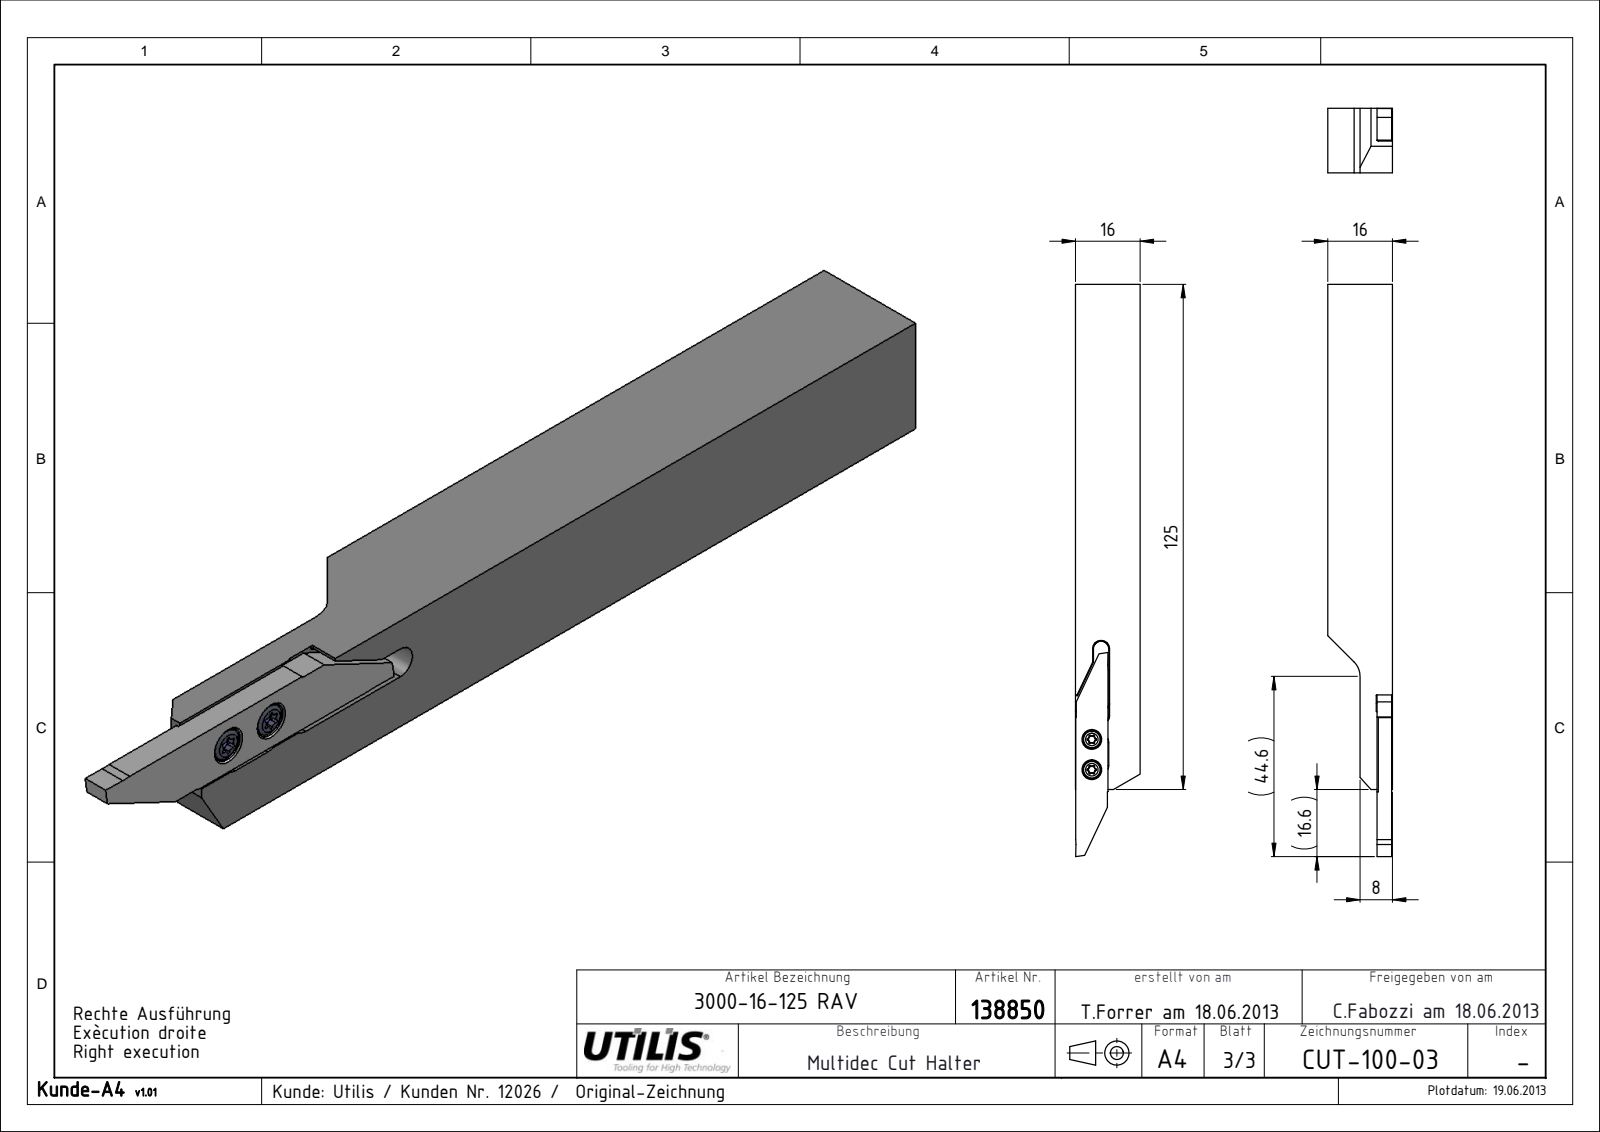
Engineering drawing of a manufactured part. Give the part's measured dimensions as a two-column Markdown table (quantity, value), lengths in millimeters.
| quantity | value |
| --- | --- |
| part name | CUT-100-03 |
| STEP written by | SolidWorks 2016 (AUTOMOTIVE_DESIGN) |
| units | millimeters |
| bodies | 1 solid, 77 faces (35 planar, 38 cylindrical, 4 other) |
| overall size | 141.6 × 16 × 16 |
| volume | 27 690 mm³ |
| surface area | 8 417 mm² |
| partial cylindrical surfaces (radius × count) | 0.2 × 12, 0.45 × 12, 2.1 × 4, 10 × 2, 5 × 1 |
| main face-to-face distances | 16, 8, 15.8, 7.8, 4.2, 3.8, 12.2, 3.6, 15.95, 7.95 |
